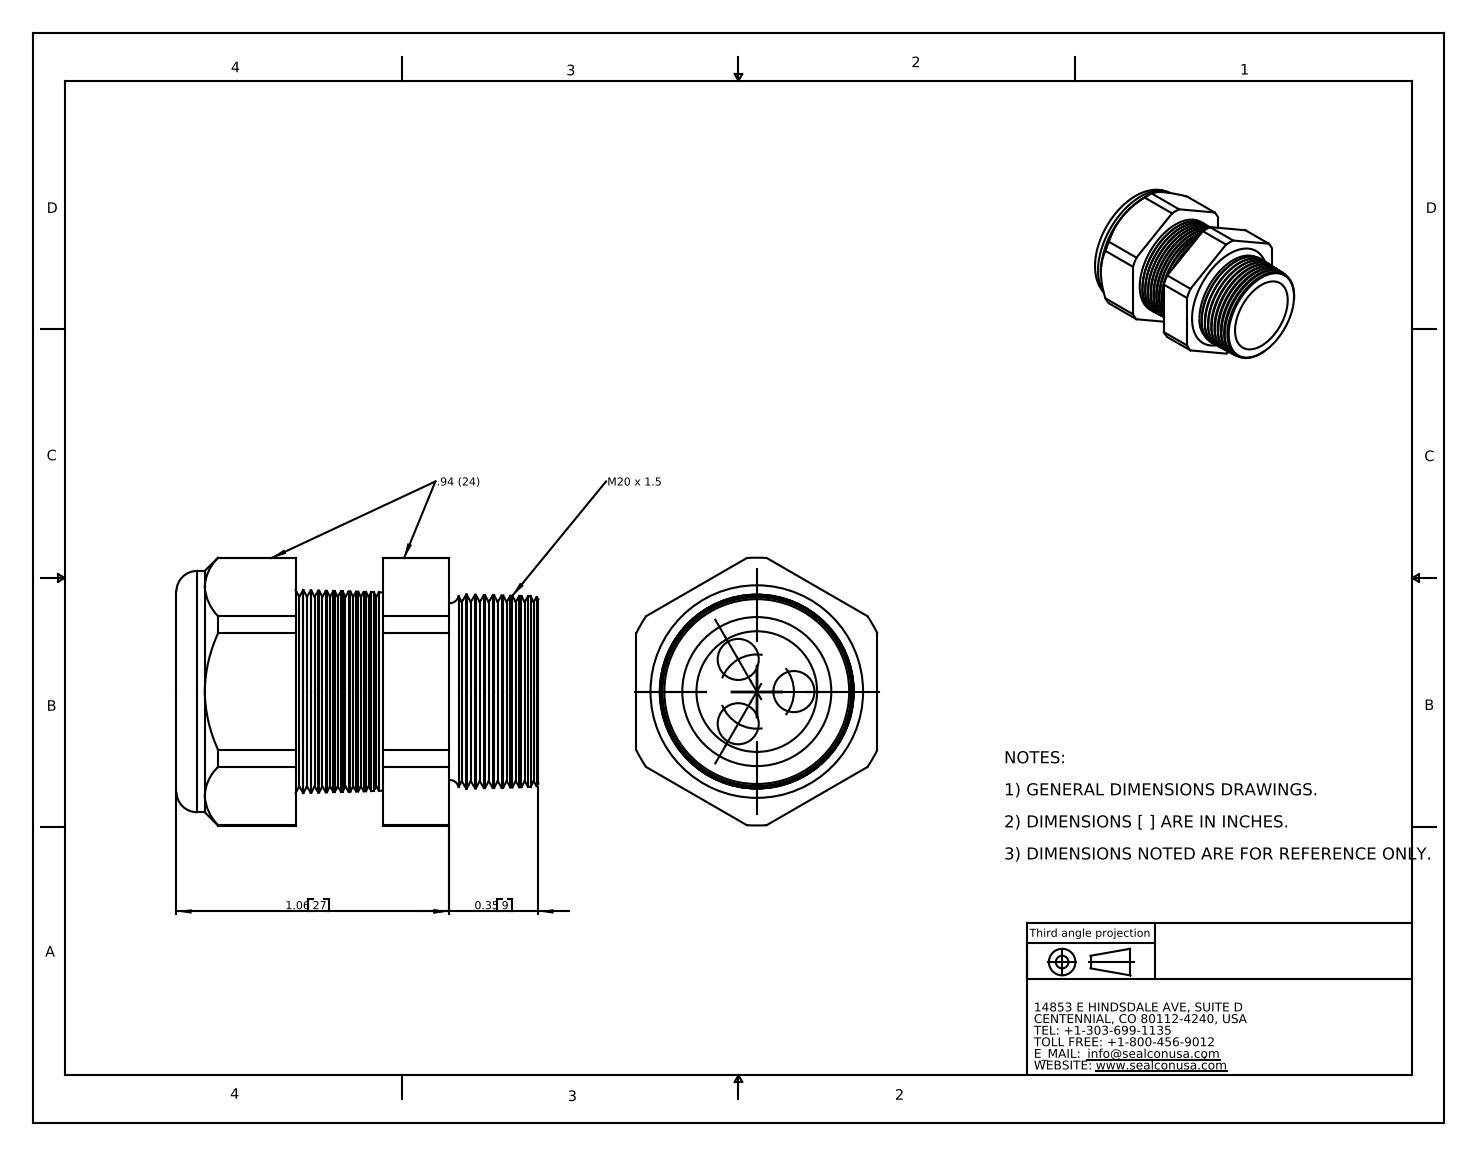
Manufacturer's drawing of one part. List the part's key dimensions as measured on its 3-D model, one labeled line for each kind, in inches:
Part name (STEP PRODUCT): CD20M3-BK
STEP written by: SolidWorks 2007 (CONFIG_CONTROL_DESIGN)
Units: inches
Bodies: 2 solids, 180 faces (20 planar, 26 cylindrical, 134 other)
Overall size (bounding box): 1.41 × 1.043 × 0.94
Volume: 0.572 in³ · Surface area: 9.967 in²
Round holes (diameter × count): ⌀0.16 ×3, ⌀0.45 ×1, ⌀0.47 ×1
Round bosses / shafts (diameter × count): ⌀0.94 ×1
Partial cylindrical surfaces — rounded edges, fillets, slot ends (radius × count): R0.522 ×1
Main face-to-face distances: 0.94, 0.804, 0.465, 0.34, 1.06, 0.596, 0.256, 1.41, 0.946, 0.606
Hole centre spacings: 0.144, 0.25
